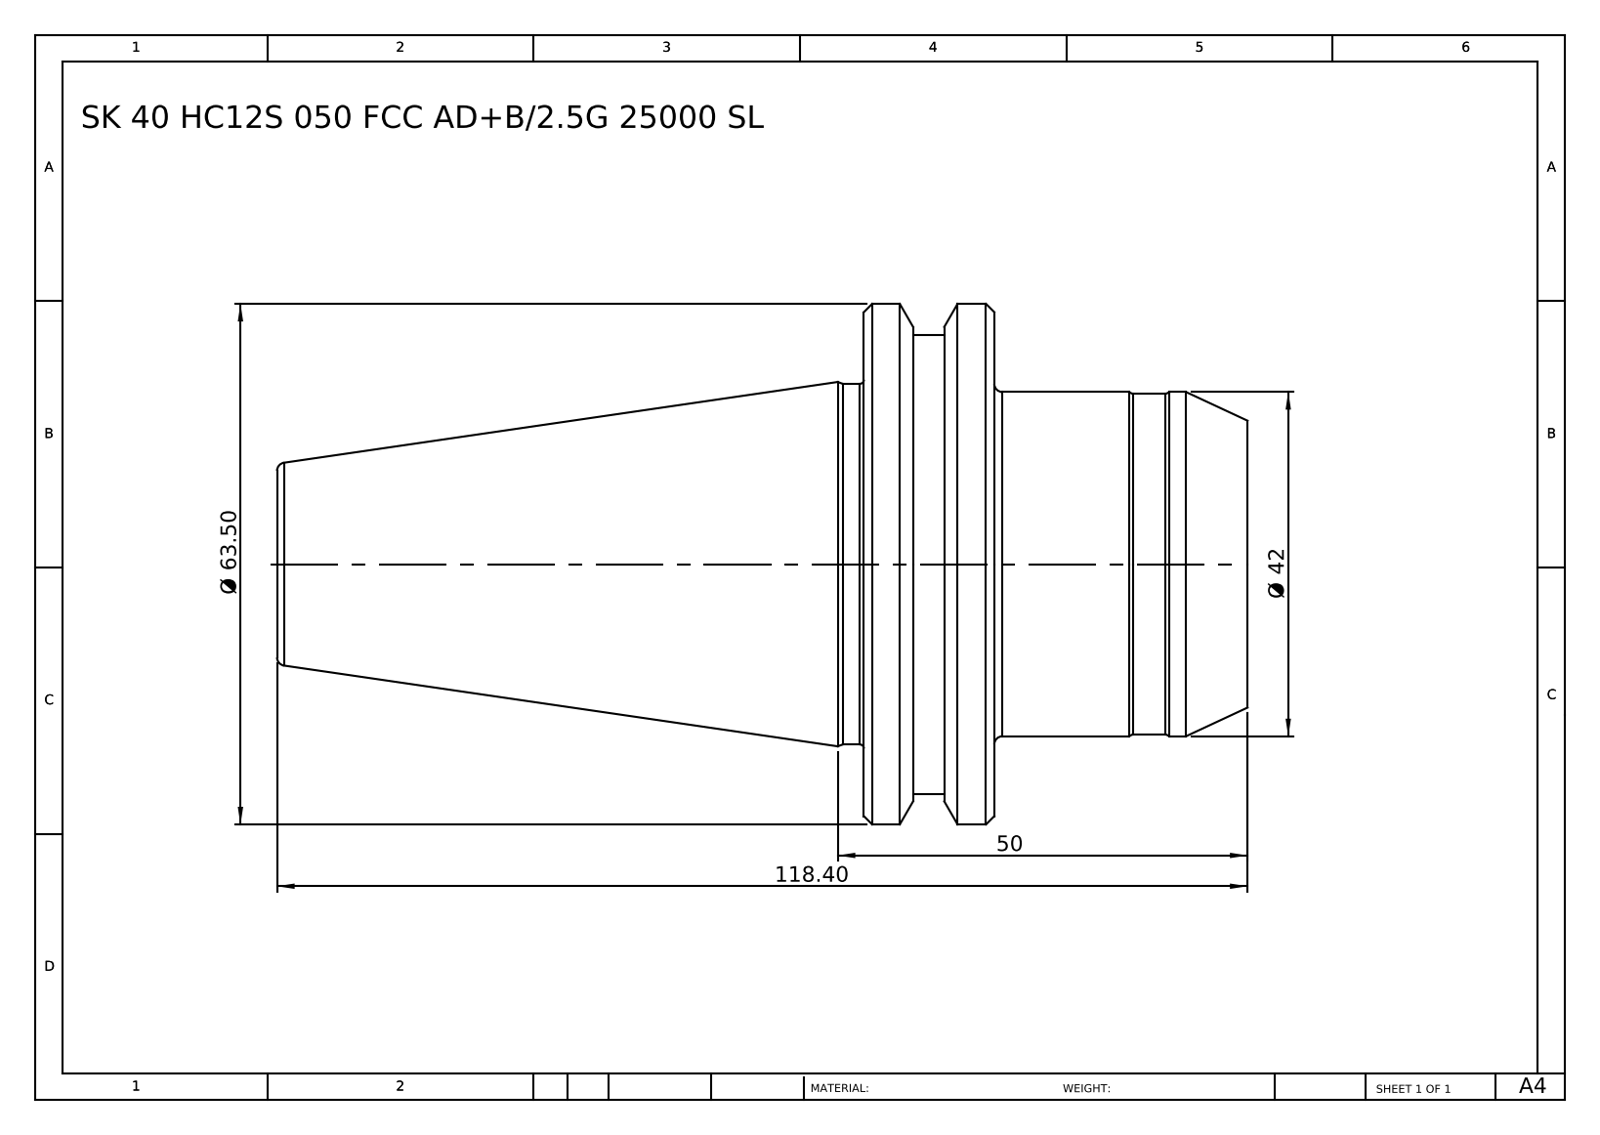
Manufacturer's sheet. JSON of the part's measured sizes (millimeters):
{"part_name": "SK 40 HC12S 050 FCC AD+B -2.5G 25000 SL", "step_written_by": "SolidWorks 2014 (CONFIG_CONTROL_DESIGN)", "units": "millimeters", "bodies": {"solids": 1, "faces": 44, "planar": 6, "cylindrical": 14, "other": 24}, "overall_size": [118.4, 63.5, 63.5], "volume_mm3": 158157, "surface_area_mm2": 20555, "round_bosses_or_shafts": [[63.5, 1], [56, 1], [44, 1], [42, 1], [41.5, 1]], "face_to_face_distances": [15.9, 30.9, 46.8, 118.4, 87.5, 71.6, 37, 6.1, 9.8, 81.4]}
